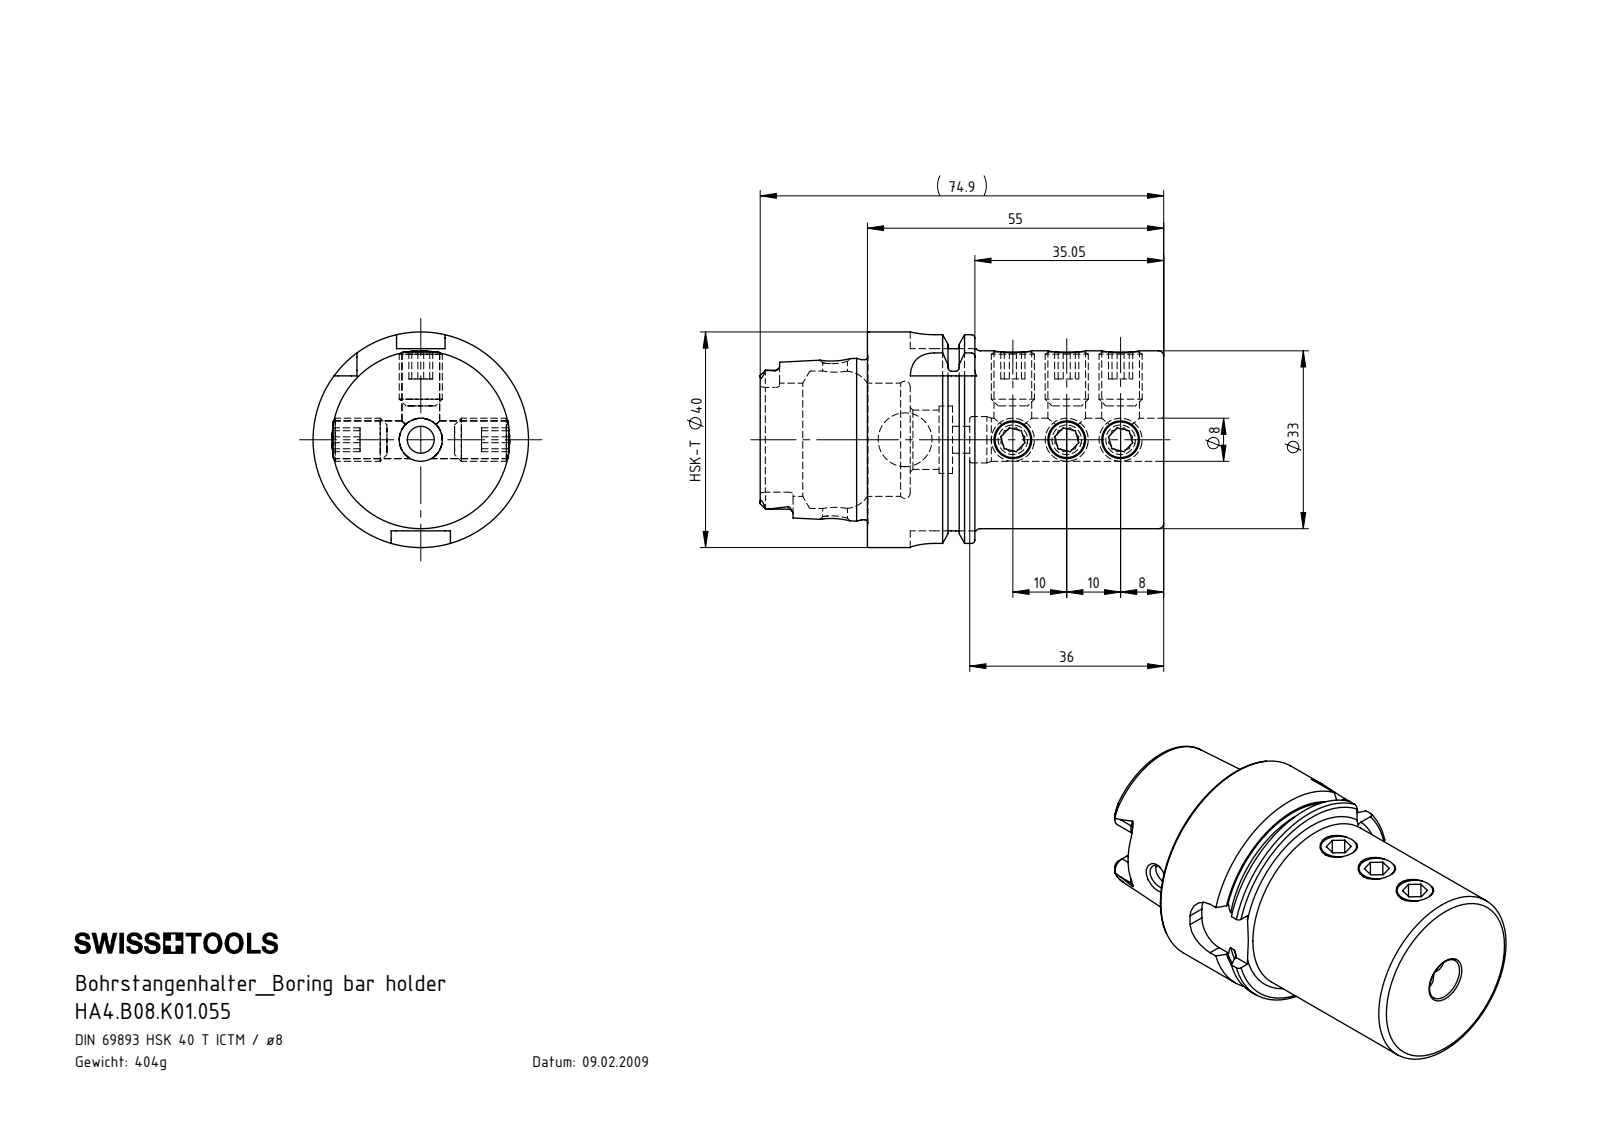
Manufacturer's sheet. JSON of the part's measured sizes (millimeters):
{"part_name": "HA4.B08.K01.055; HA4-B08.K01.055_C_Fertigbearbeitung; ISO 4026 - M8 x 10_PreviewCfg", "step_written_by": "SolidWorks 2017 (AUTOMOTIVE_DESIGN)", "units": "millimeters", "bodies": {"solids": 10, "faces": 322, "planar": 128, "cylindrical": 89, "other": 105}, "overall_size": [74.9, 40, 40], "volume_mm3": 51494, "surface_area_mm2": 19397, "round_holes": [[7, 6], [4.6, 1], [5, 1], [8, 1], [8.6, 1], [10, 1], [11, 1], [12.5, 1], [21, 1], [25.5, 1]], "round_bosses_or_shafts": [[8, 6], [40, 1], [34.75, 1], [33, 1], [29.71, 1]], "partial_cylinders_radius": [[0.9, 6], [1.88, 4], [4.5, 4]], "face_to_face_distances": [55, 4, 5, 10, 7.95, 47.05, 19.95, 12, 35.05, 22.56], "hole_center_spacings": [10, 20, 30, 33, 40, 43, 53]}
